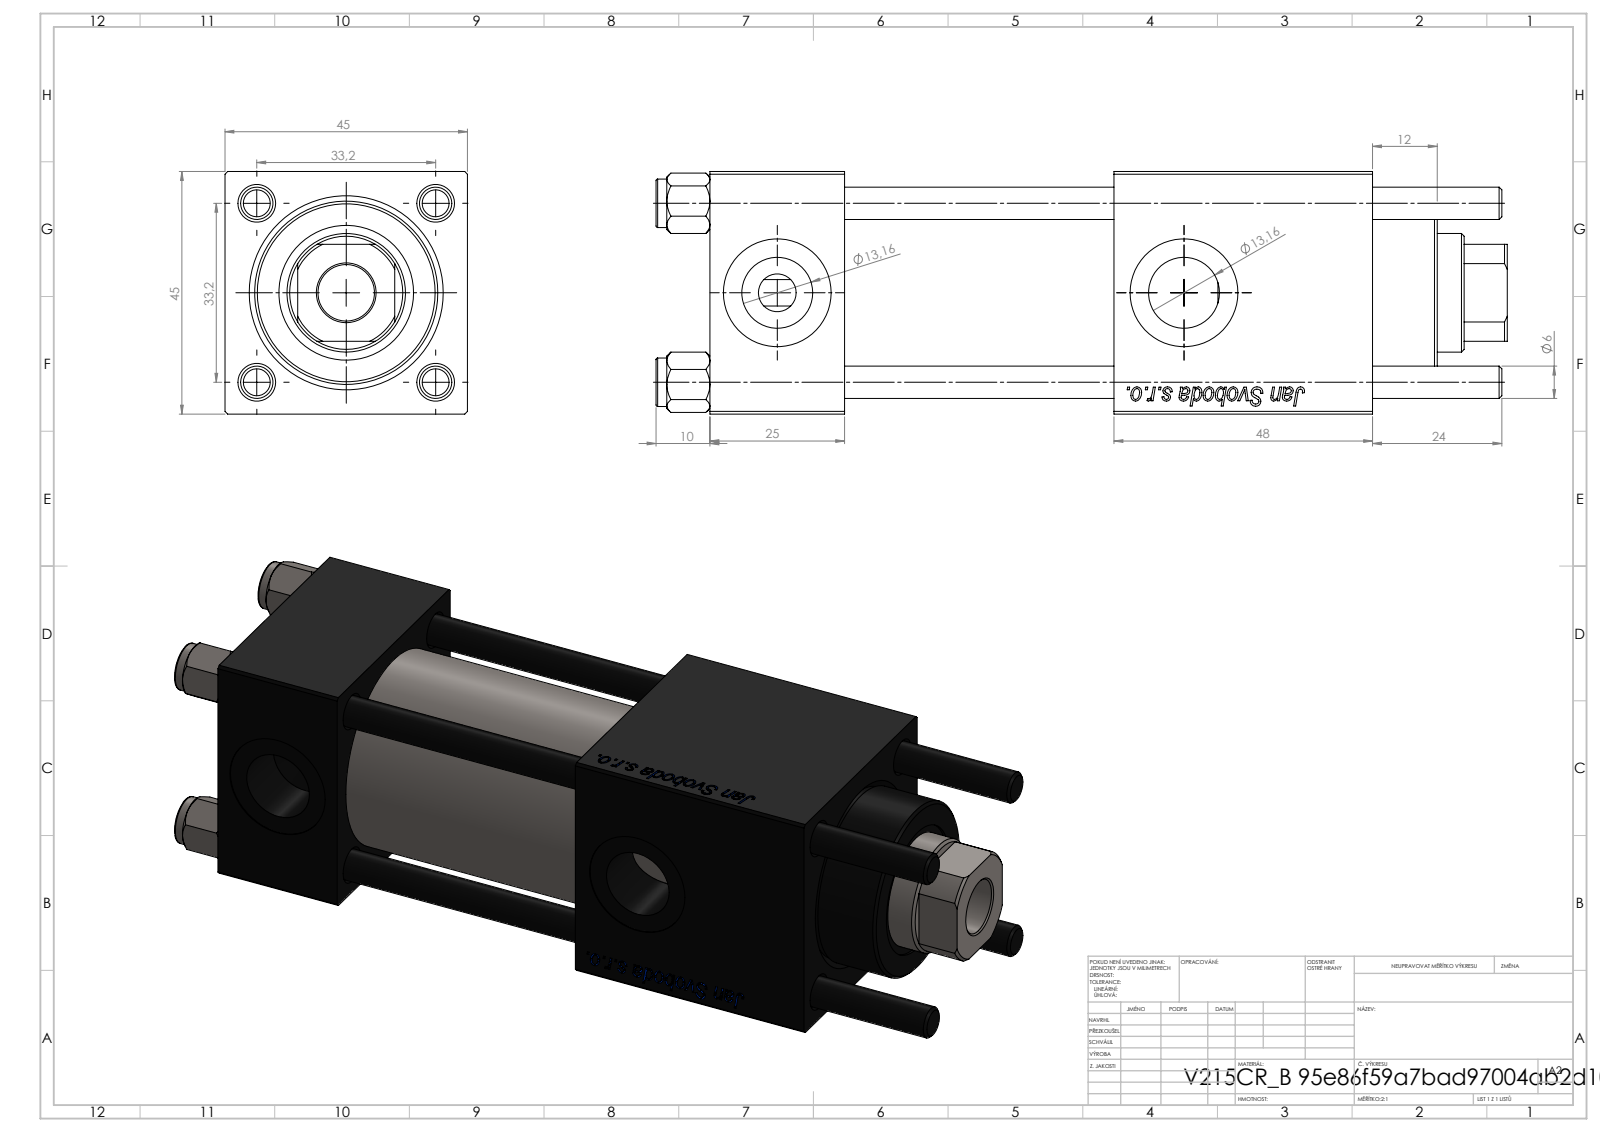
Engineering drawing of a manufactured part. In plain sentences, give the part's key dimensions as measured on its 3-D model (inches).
The part is named "V215CR_B-1; V215_VC_A; V215CR_B_TYCINKA; NUT_M5_B (+1 more)". Its 3-D file was written by "SolidWorks 2019 (CONFIG_CONTROL_DESIGN)". It is 11 solids with 1157 faces: 431 planar, 78 cylindrical and 648 other. Overall it measures 6.22 by 1.772 by 1.772 inches. Its volume is 13.08 cubic inches and its surface area 119 square inches. Round holes: 4 of diameter 0.236, 2 of diameter 0.276, 2 of diameter 0.518, 2 of diameter 0.787, 1 of diameter 0.413, 1 of diameter 0.866, 1 of diameter 0.945, 1 of diameter 0.984, 1 of diameter 1.26, 1 of diameter 1.299. Round bosses or shafts: 4 of diameter 0.354, 1 of diameter 1.496, 1 of diameter 1.339. Partial cylindrical surfaces (rounded edges, fillets, slot ends): 1 of radius 0.413. The main face-to-face distances are 1.772, 0.984, 1.969, 4.843, 2.953, 3.858, 1.89, 3.713, 2.728, 0.76. The hole center spacings are 0.924, 1.307, 1.848, 2.972.
